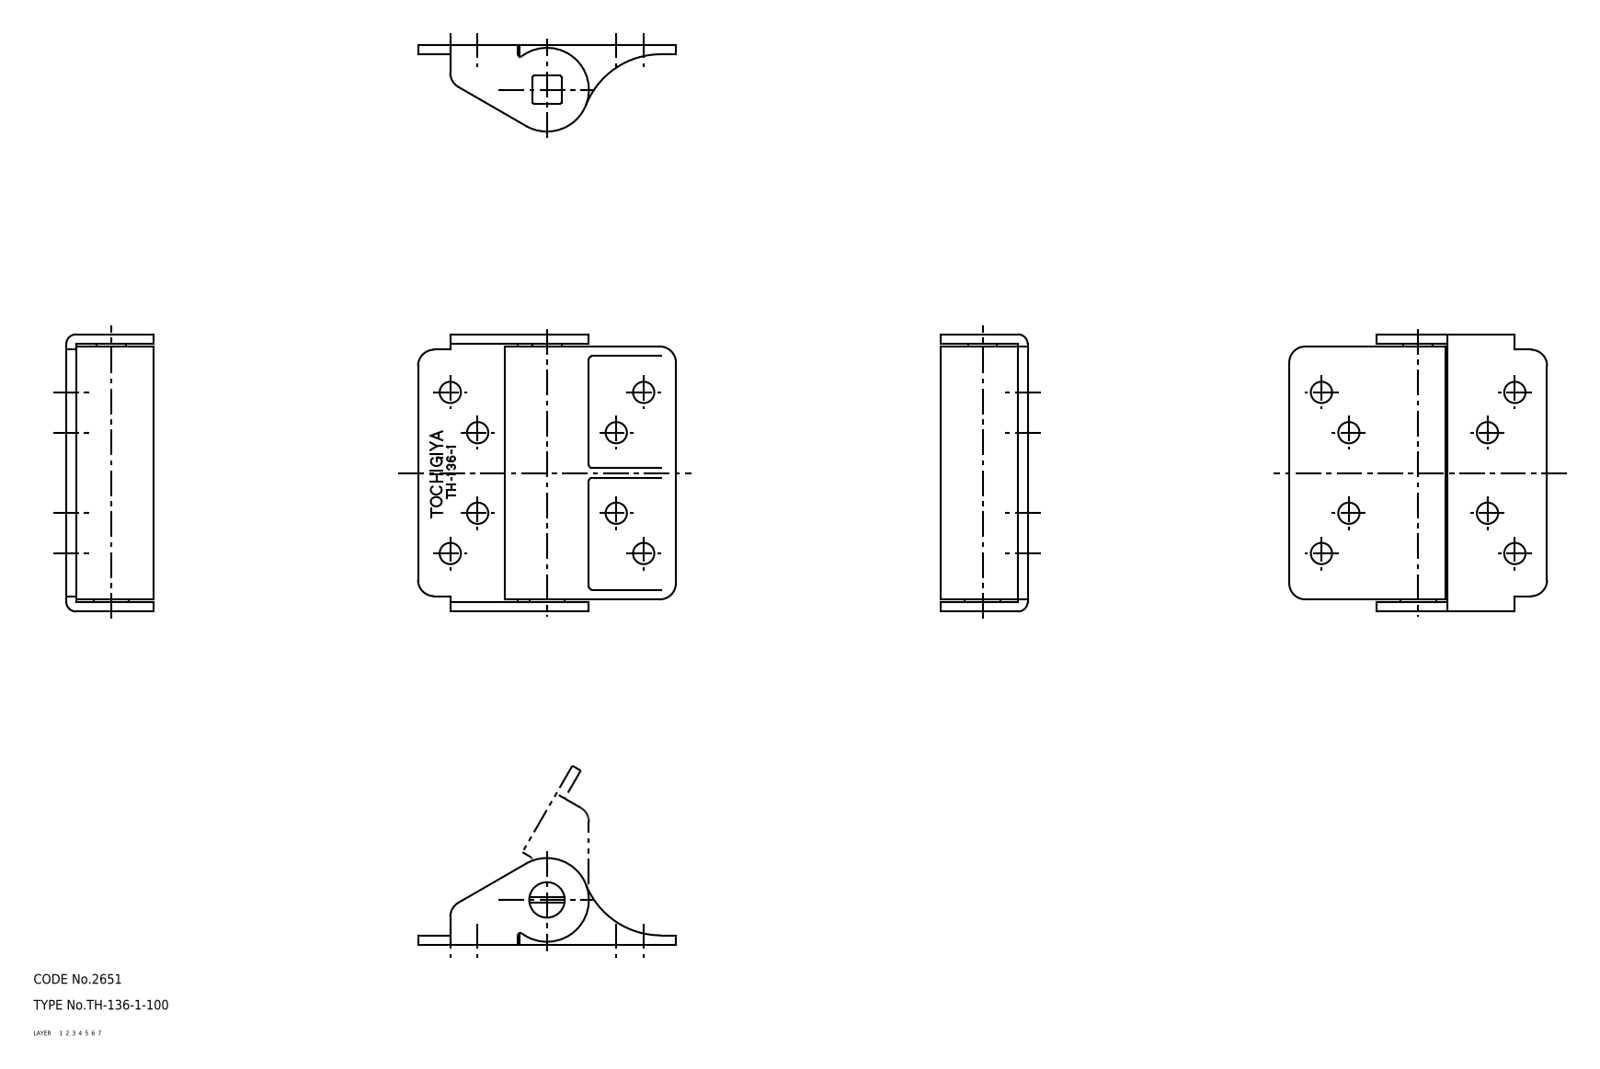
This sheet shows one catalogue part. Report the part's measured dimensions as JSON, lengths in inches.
{"part_name": "TH_136_1_100; hinge piece; needle; shaft", "step_written_by": "SolidWorks 2015 (AUTOMOTIVE_DESIGN)", "units": "inches", "bodies": {"solids": 4, "faces": 115, "planar": 51, "cylindrical": 60, "other": 4}, "overall_size": [3.386, 3.15, 1.063], "volume_in3": 4.009, "surface_area_in2": 43.7, "round_holes": [[0.26, 8], [0.098, 1], [0.433, 1]], "round_bosses_or_shafts": [[1.024, 1]], "partial_cylinders_radius": [[0.039, 9], [0.197, 5], [0.118, 2], [0.03, 1], [0.236, 1], [0.984, 1]], "face_to_face_distances": [0.118, 0.148, 3.12, 3.238, 3.268, 0.03, 3.15, 3.386, 3.091, 0.846], "hole_center_spacings": [0.595, 1.514, 2.087, 2.508, 0.984, 1.693, 1.958, 1.969]}
